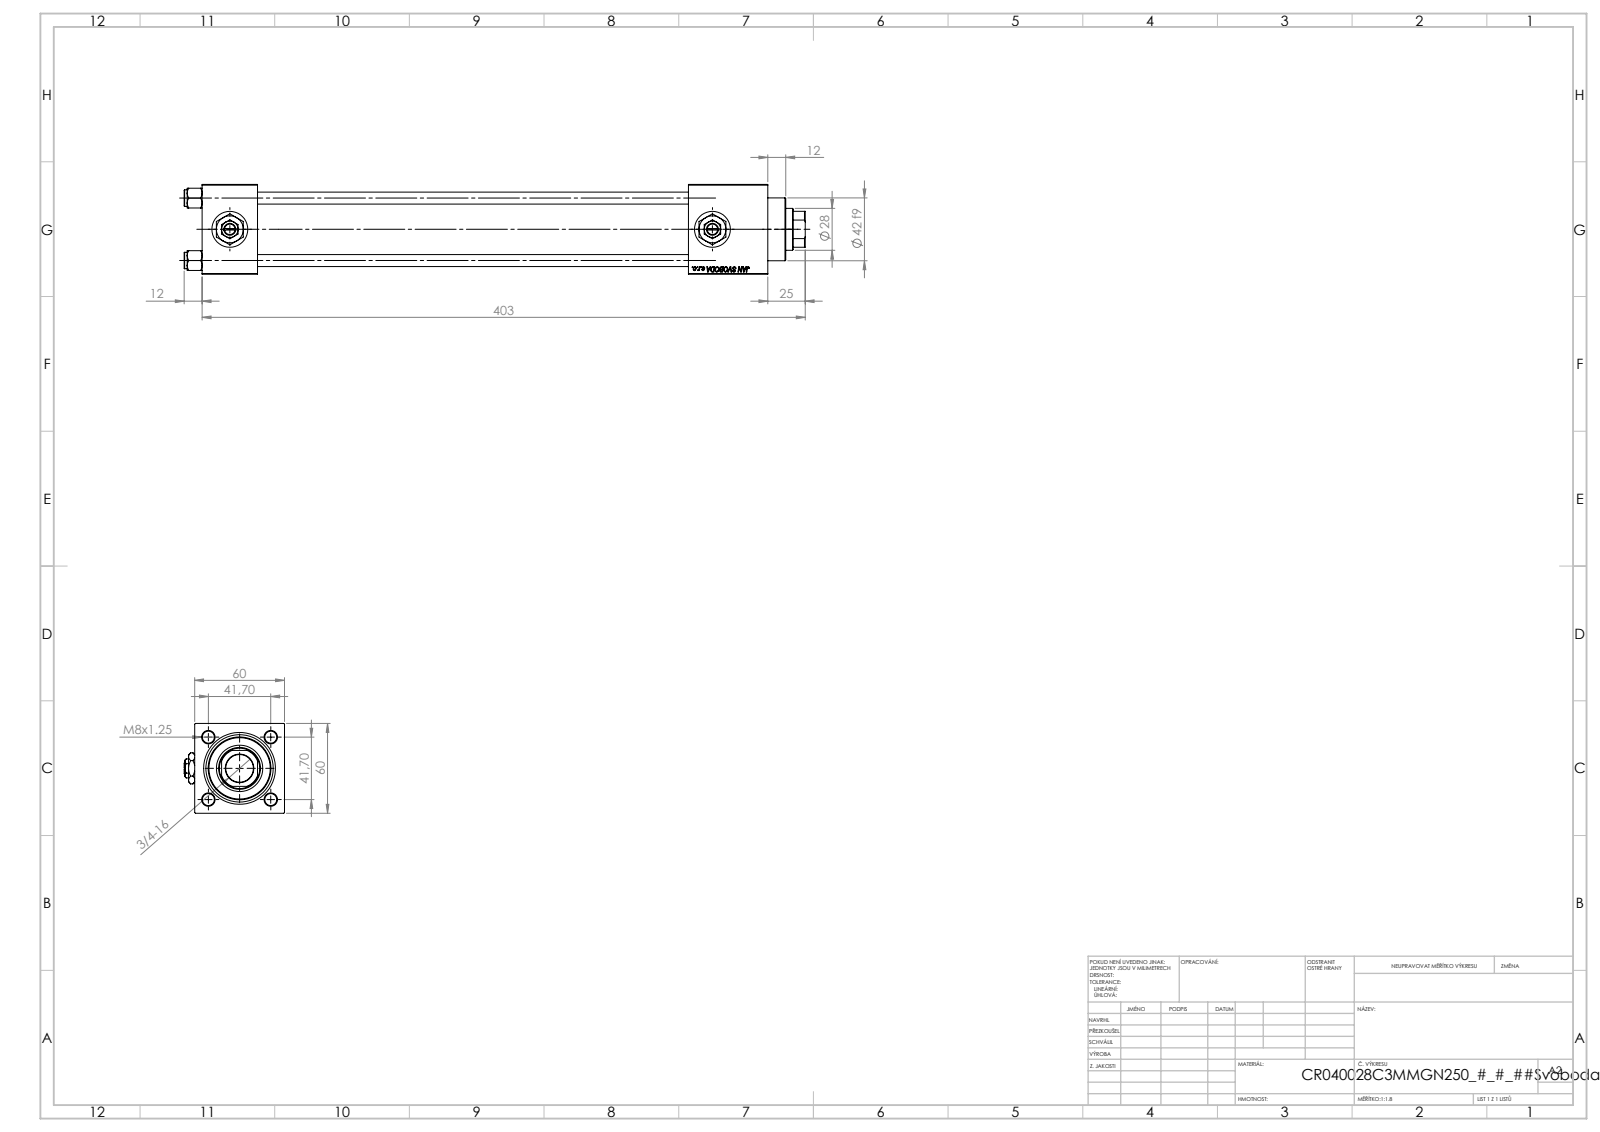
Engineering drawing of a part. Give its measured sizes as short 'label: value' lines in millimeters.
name: V215CR_VCP_C; V215_VC_A; Zatka_pro_OIL_PORT; NUT_M5_C (+2 more)
written by: SolidWorks 2019 (CONFIG_CONTROL_DESIGN)
unit: mm
bodies: 13 solids, 1250 faces (574 planar, 98 cylindrical, 578 other)
size: 415 × 67 × 60
volume: 702 016 mm³; area: 219 845 mm²
holes: 4× ⌀8, 2× ⌀7, 2× ⌀16.66, 2× ⌀24, 1× ⌀18.5, 1× ⌀28, 1× ⌀31, 1× ⌀40, 1× ⌀45
bosses: 4× ⌀11, 1× ⌀46, 1× ⌀42
rounds: 1× R13.5
face distances: 60, 37, 325, 288, 53, 349.3, 312.3, 24.3, 378, 341
hole spacings: 29.49, 41.7, 58.97, 322.5
